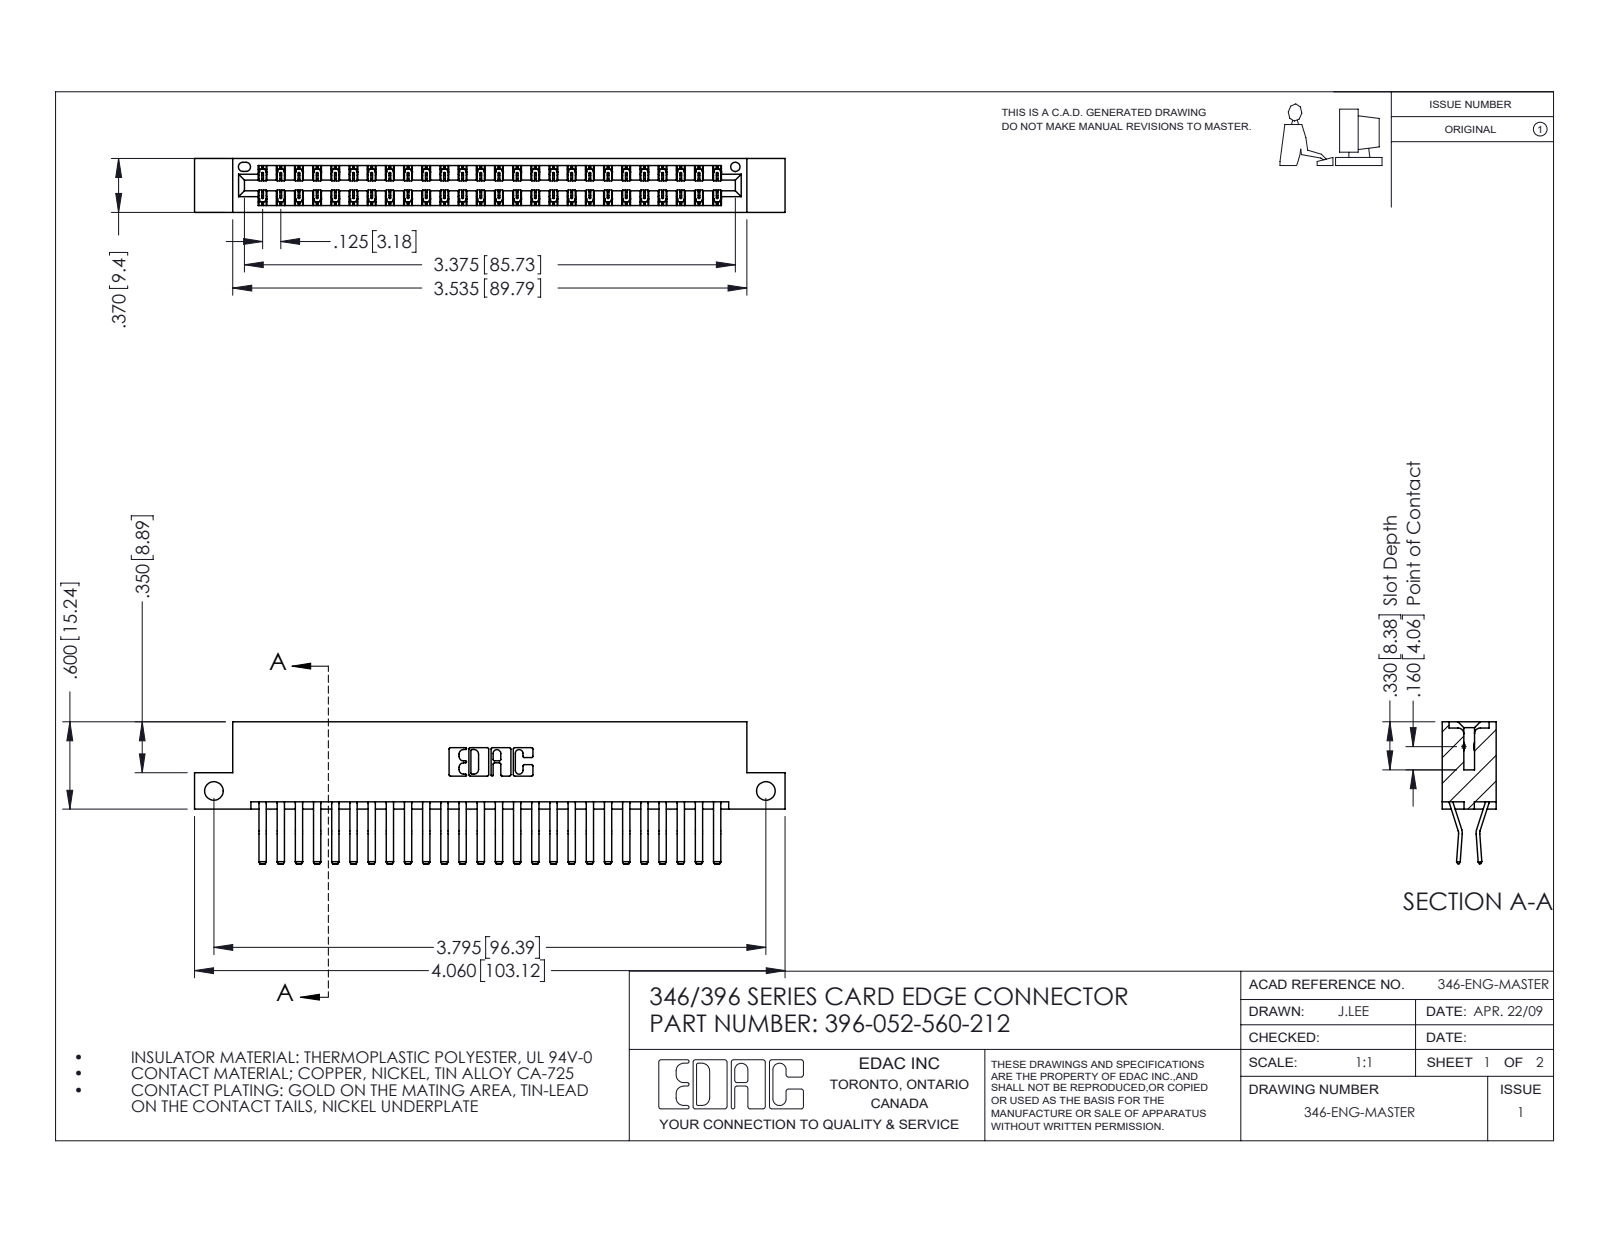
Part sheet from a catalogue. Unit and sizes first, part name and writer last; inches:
Units: inches
Overall size (bounding box): 4.06 × 0.975 × 0.37
Round holes (diameter × count): ⌀0.128 ×2, ⌀0.064 ×1
Partial cylindrical surfaces — rounded edges, fillets, slot ends (radius × count): R0.006 ×78, R0.01 ×22, R0.007 ×6, R0.031 ×6, R0.026 ×3, R0.01 ×2, R0.014 ×2, R0.022 ×2
Main face-to-face distances: 0.048, 0.322, 0.25, 0.37, 0.025, 0.072, 0.298, 0.275, 0.148, 0.222
Hole centre spacings: 3.795
Volume: 0.622 in³ · Surface area: 22.51 in²
Bodies: 53 solids, 2930 faces (1896 planar, 1034 cylindrical, 0 other)
Part name (STEP PRODUCT): 396-052-560-212; 346 Part_Flush Mounting Lugs - Side Mount; 345-292-001_560 Tail
STEP written by: SolidWorks 2016 (CONFIG_CONTROL_DESIGN)
